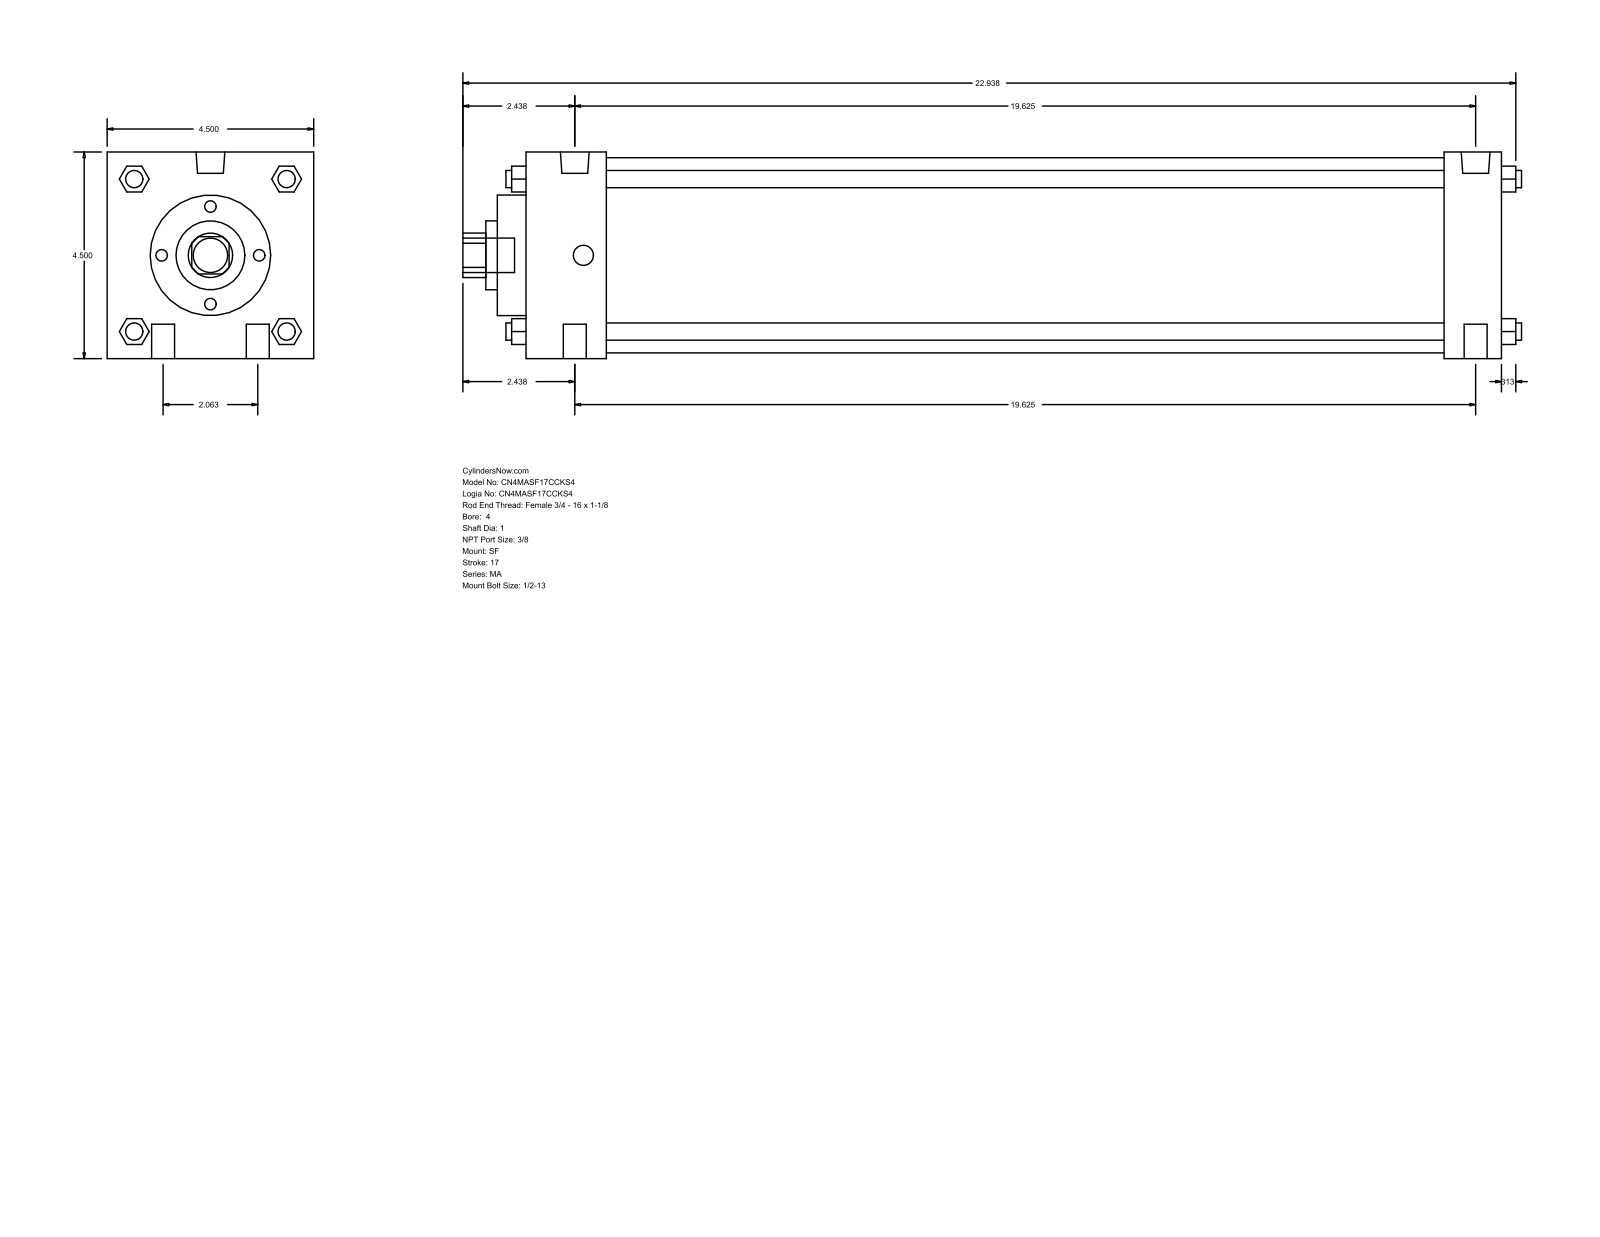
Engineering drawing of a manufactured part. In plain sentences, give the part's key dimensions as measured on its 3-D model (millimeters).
The part is named "MA_SF__0400_1". Its 3-D file was written by "GSSL Pune (CONFIG_CONTROL_DESIGN)". It is 0 solids with 126 faces: 95 planar, 31 cylindrical and 0 other. Overall it measures 585.79 by 114.3 by 114.3 millimeters. Round holes: 1 of diameter 25.4, 1 of diameter 38.1, 1 of diameter 66.67, 1 of diameter 107.95. Round bosses or shafts: 4 of diameter 12.7, 4 of diameter 9.53, 2 of diameter 15.93, 2 of diameter 11.11, 1 of diameter 19.05. Partial cylindrical surfaces (rounded edges, fillets, slot ends): 1 of radius 12.29. The main face-to-face distances are 114.3, 539.75, 508, 31.75, 44.46, 463.54, 495.29, 555.62, 15.87, 60.33.
